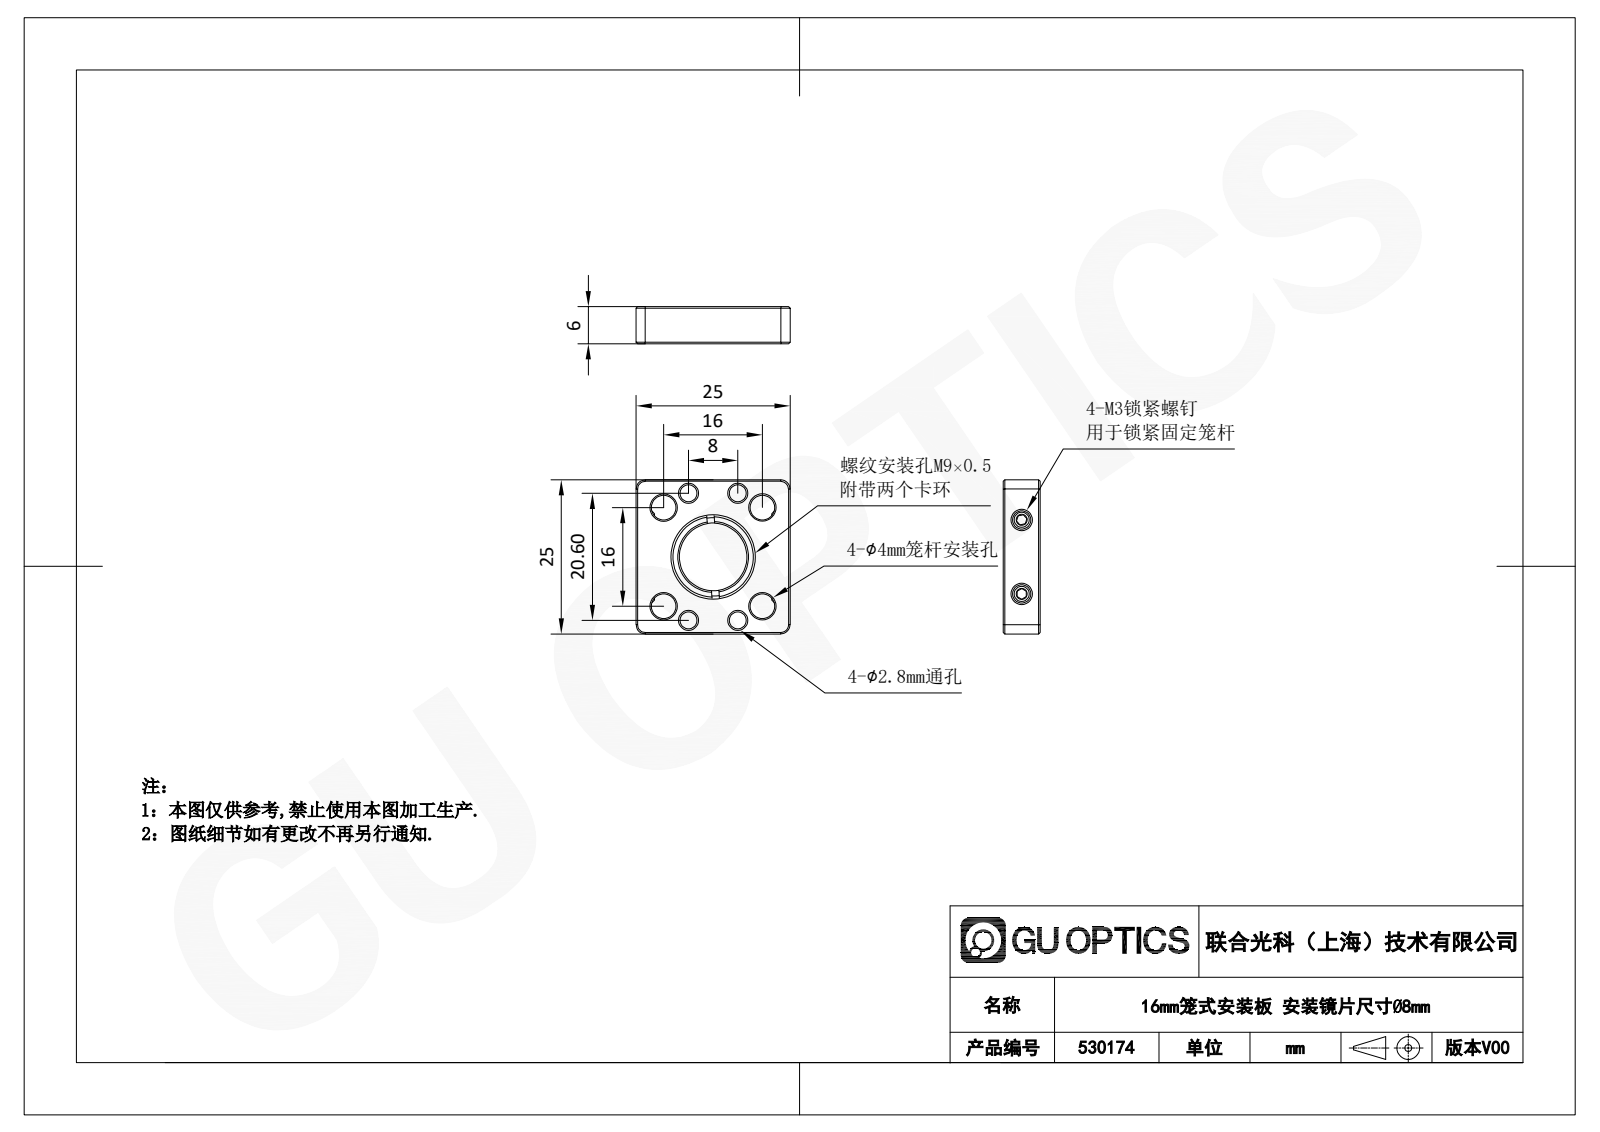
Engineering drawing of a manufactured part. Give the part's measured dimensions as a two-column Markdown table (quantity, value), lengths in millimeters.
| quantity | value |
| --- | --- |
| part name | 530174 |
| STEP written by | SolidWorks 2020 (CONFIG_CONTROL_DESIGN) |
| units | millimeters |
| bodies | 7 solids, 288 faces (141 planar, 25 cylindrical, 122 other) |
| overall size | 25 × 25 × 6 |
| volume | 3 023 mm³ |
| surface area | 2 716 mm² |
| round holes (diameter × count) | 2.8 × 4, 4 × 4, 2.5 × 2, 6.5 × 1, 8.5 × 1 |
| round bosses / shafts (diameter × count) | 3 × 2, 9 × 1 |
| partial cylindrical surfaces (radius × count) | 1.5 × 4 |
| main face-to-face distances | 6, 25, 2, 4, 21.56, 3, 22, 1.5, 1, 24 |
| hole center spacings | 4.61, 11.05, 11.31, 12.22, 16, 18.73, 21.88, 8 |
